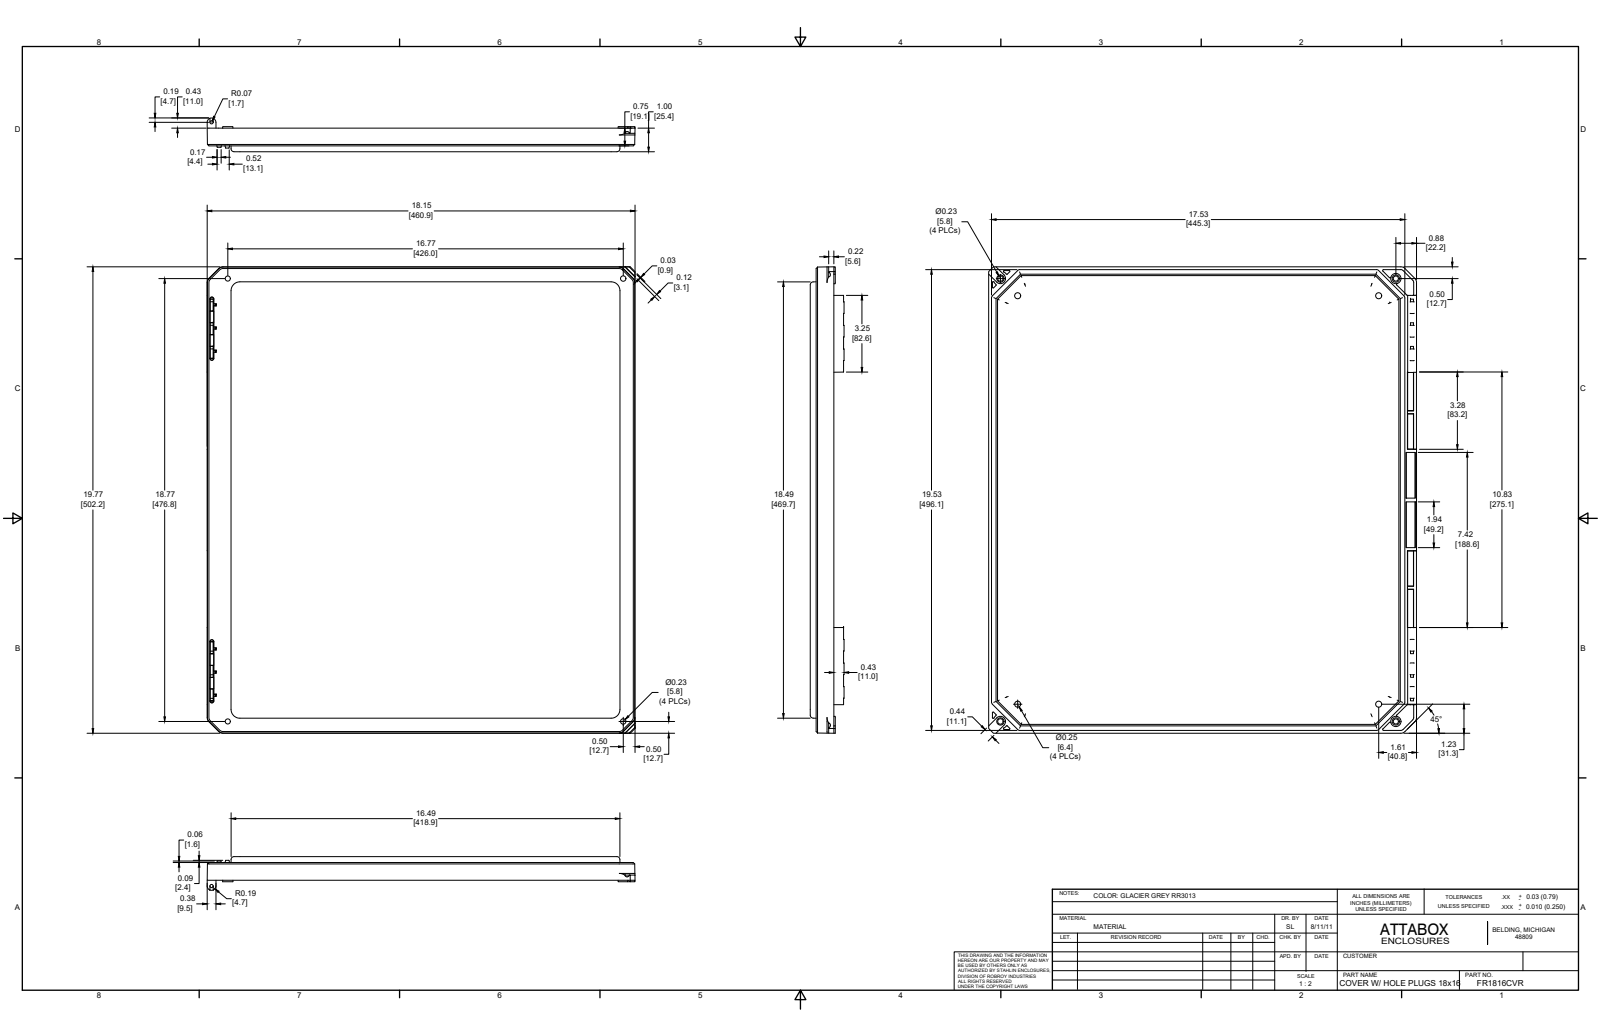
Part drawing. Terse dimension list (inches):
name: FR1816CVR
written by: SolidWorks 2019 (AUTOMOTIVE_DESIGN)
unit: in
bodies: 1 solid, 626 faces (266 planar, 200 cylindrical, 160 other)
size: 19.772 × 18.147 × 1.434
volume: 65.61 in³; area: 891 in²
holes: 4× ⌀0.253, 2× ⌀0.219, 2× ⌀0.227, 2× ⌀0.313, 1× ⌀0.137
bosses: 2× ⌀0.435
rounds: 27× R0.03, 18× R0.01, 16× R0.096, 13× R0.063, 12× R0.125, 11× R0.06, 11× R0.062, 10× R0.04
face distances: 0.125, 0.25, 0.125, 0.375, 0.75, 0.375, 0.625, 1, 0.875, 0.25
hole spacings: 1.033, 1.033, 15.311, 16.057, 16.059, 16.772, 17.311, 18.056
